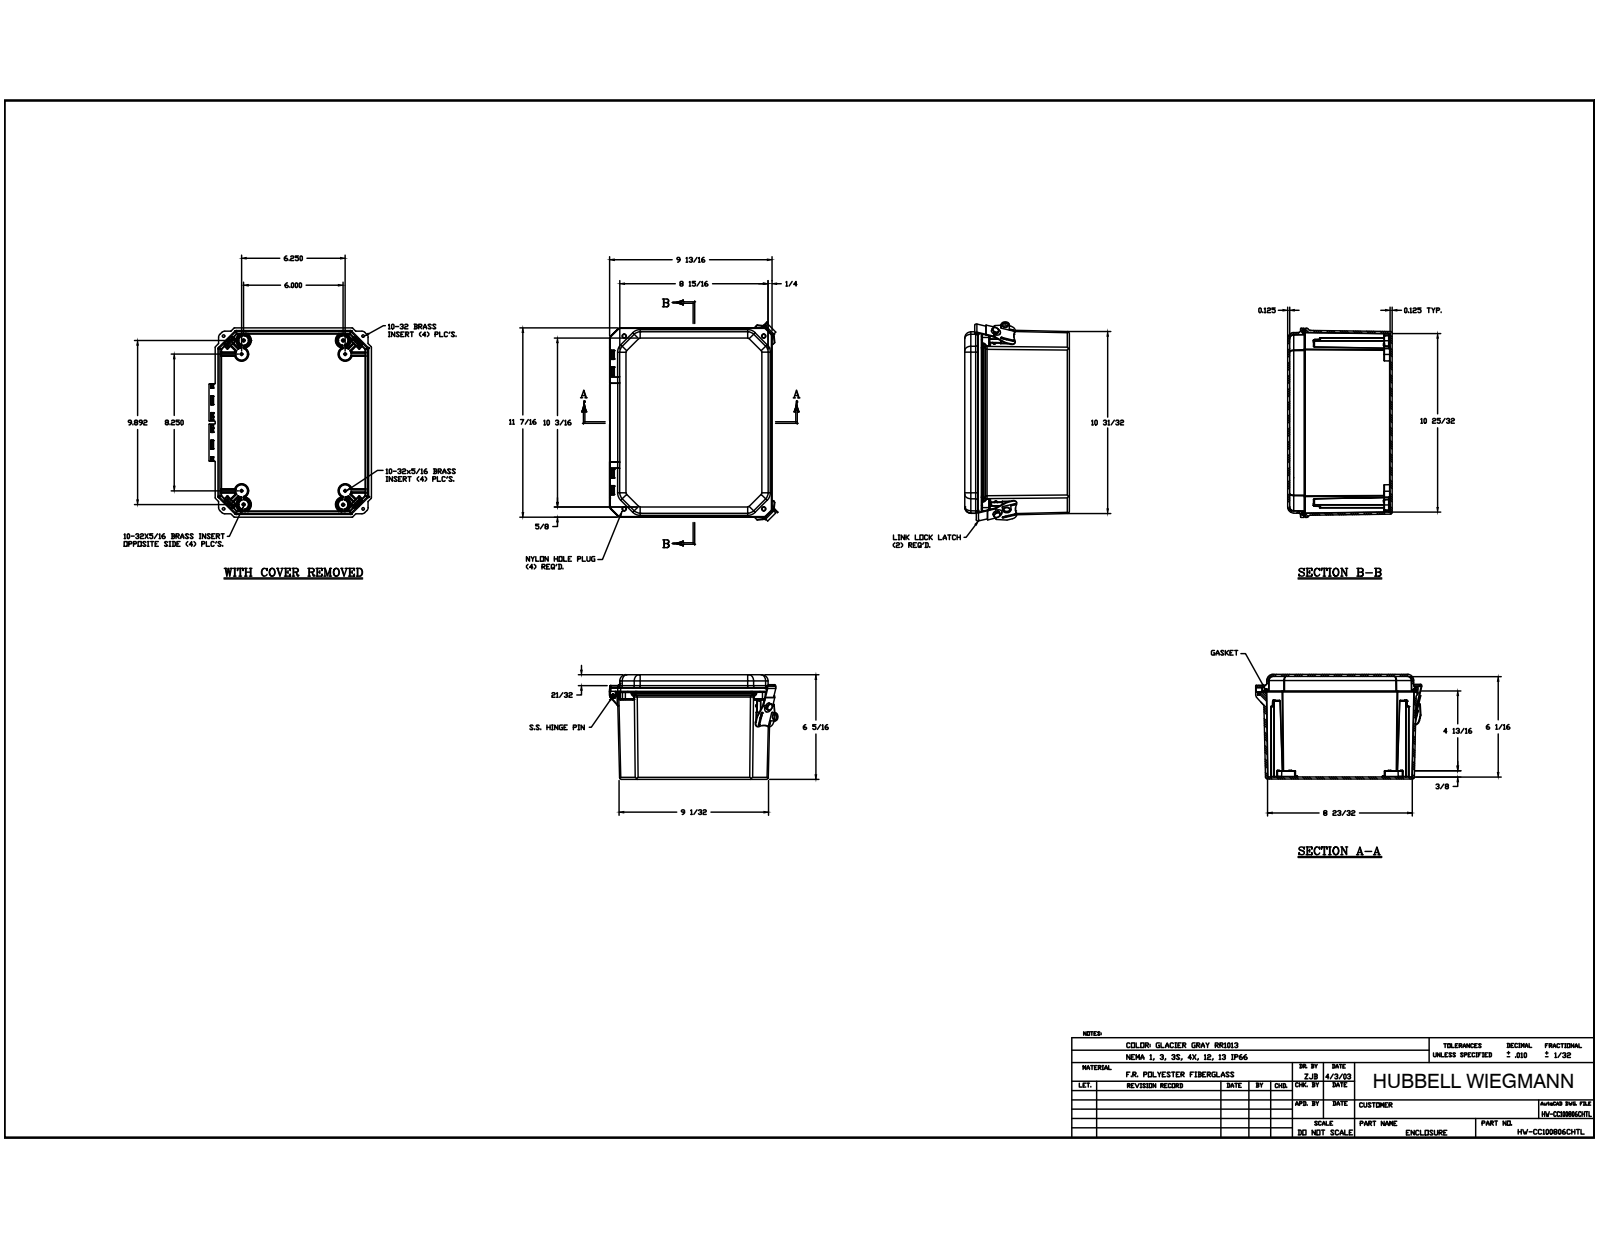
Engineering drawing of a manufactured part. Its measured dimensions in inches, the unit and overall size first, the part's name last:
Units: inches
Overall size (bounding box): 12.33 × 10.254 × 6.312
Round holes (diameter × count): ⌀0.156 ×12, ⌀0.152 ×8, ⌀0.098 ×4, ⌀0.15 ×4, ⌀0.219 ×4, ⌀0.252 ×4, ⌀0.312 ×4, ⌀0.05 ×2, ⌀0.12 ×2, ⌀0.363 ×2, ⌀0.137 ×1
Round bosses / shafts (diameter × count): ⌀0.246 ×12, ⌀0.87 ×4, ⌀0.209 ×4, ⌀0.2 ×4, ⌀0.135 ×3, ⌀0.6 ×2, ⌀0.05 ×2
Partial cylindrical surfaces — rounded edges, fillets, slot ends (radius × count): R0.01 ×208, R0.005 ×94, R0.02 ×59, R0.125 ×41, R0.03 ×38, R0.039 ×28, R0.25 ×26, R0.03 ×24
Main face-to-face distances: 0.125, 6.187, 0.127, 0.126, 6.312, 6.062, 0.25, 5.531, 0.656, 1
Hole centre spacings: 10.422, 1.536, 10.35, 10.945, 0.831, 6.18, 7.416, 9.072
Volume: 63.71 in³ · Surface area: 985.4 in²
Bodies: 31 solids, 2278 faces (656 planar, 890 cylindrical, 732 other)
Part name (STEP PRODUCT): DS100806BOX; DSCC100806CVR; GA1008; WP1008HLU (+5 more)
STEP written by: Autodesk Inventor 2014 (AUTOMOTIVE_DESIGN)
